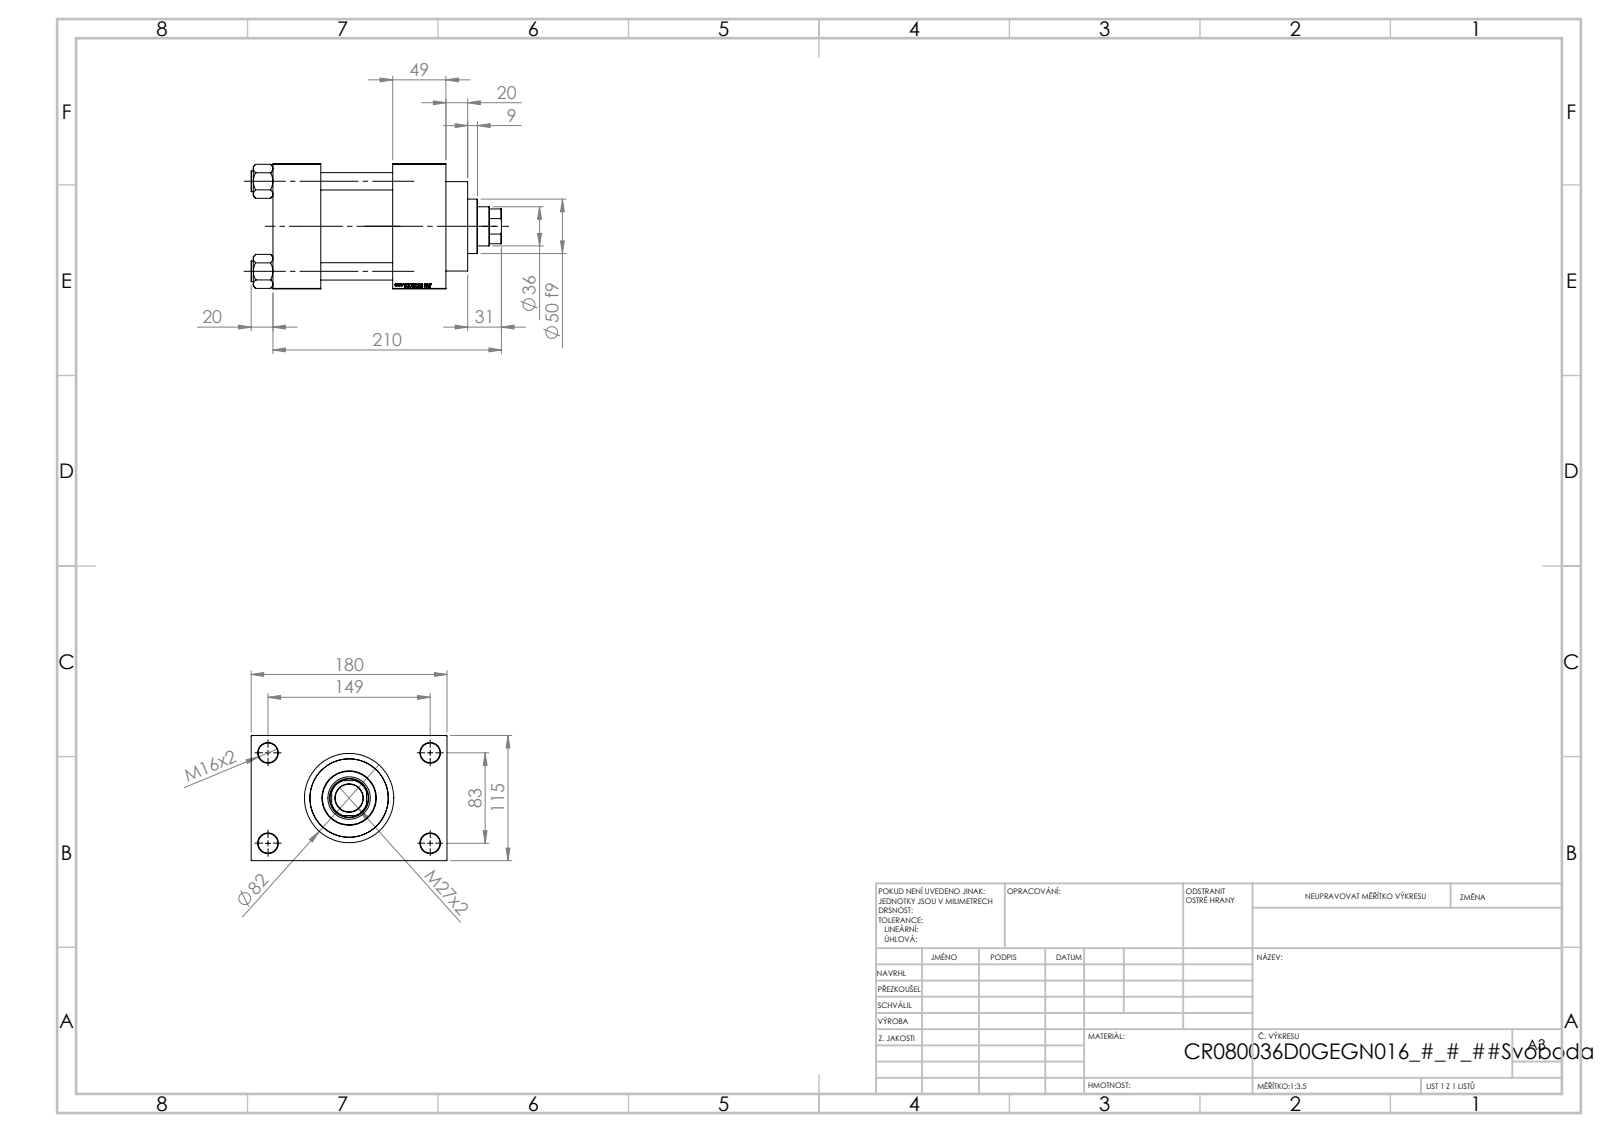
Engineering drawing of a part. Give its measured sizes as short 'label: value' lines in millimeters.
name: V215CR_D_TYCINKA; NUT_M5_D; V215CR_D_Body; V215_VC_A (+1 more)
written by: SolidWorks 2019 (CONFIG_CONTROL_DESIGN)
unit: mm
bodies: 11 solids, 1152 faces (545 planar, 89 cylindrical, 518 other)
size: 230 × 180 × 115
volume: 1 997 000 mm³; area: 293 897 mm²
holes: 4× ⌀16, 4× ⌀18, 2× ⌀7, 2× ⌀26.44, 2× ⌀35, 1× ⌀25.5, 1× ⌀36, 1× ⌀39, 1× ⌀61, 1× ⌀72, 1× ⌀80
bosses: 4× ⌀19, 1× ⌀86, 1× ⌀82, 1× ⌀50
rounds: 1× R17.5
face distances: 115, 66, 110, 49, 44, 159, 32.5, 147.5, 20, 69
hole spacings: 33.15, 58.48, 82.7, 85.28, 89.24, 115.85, 142.43, 83
